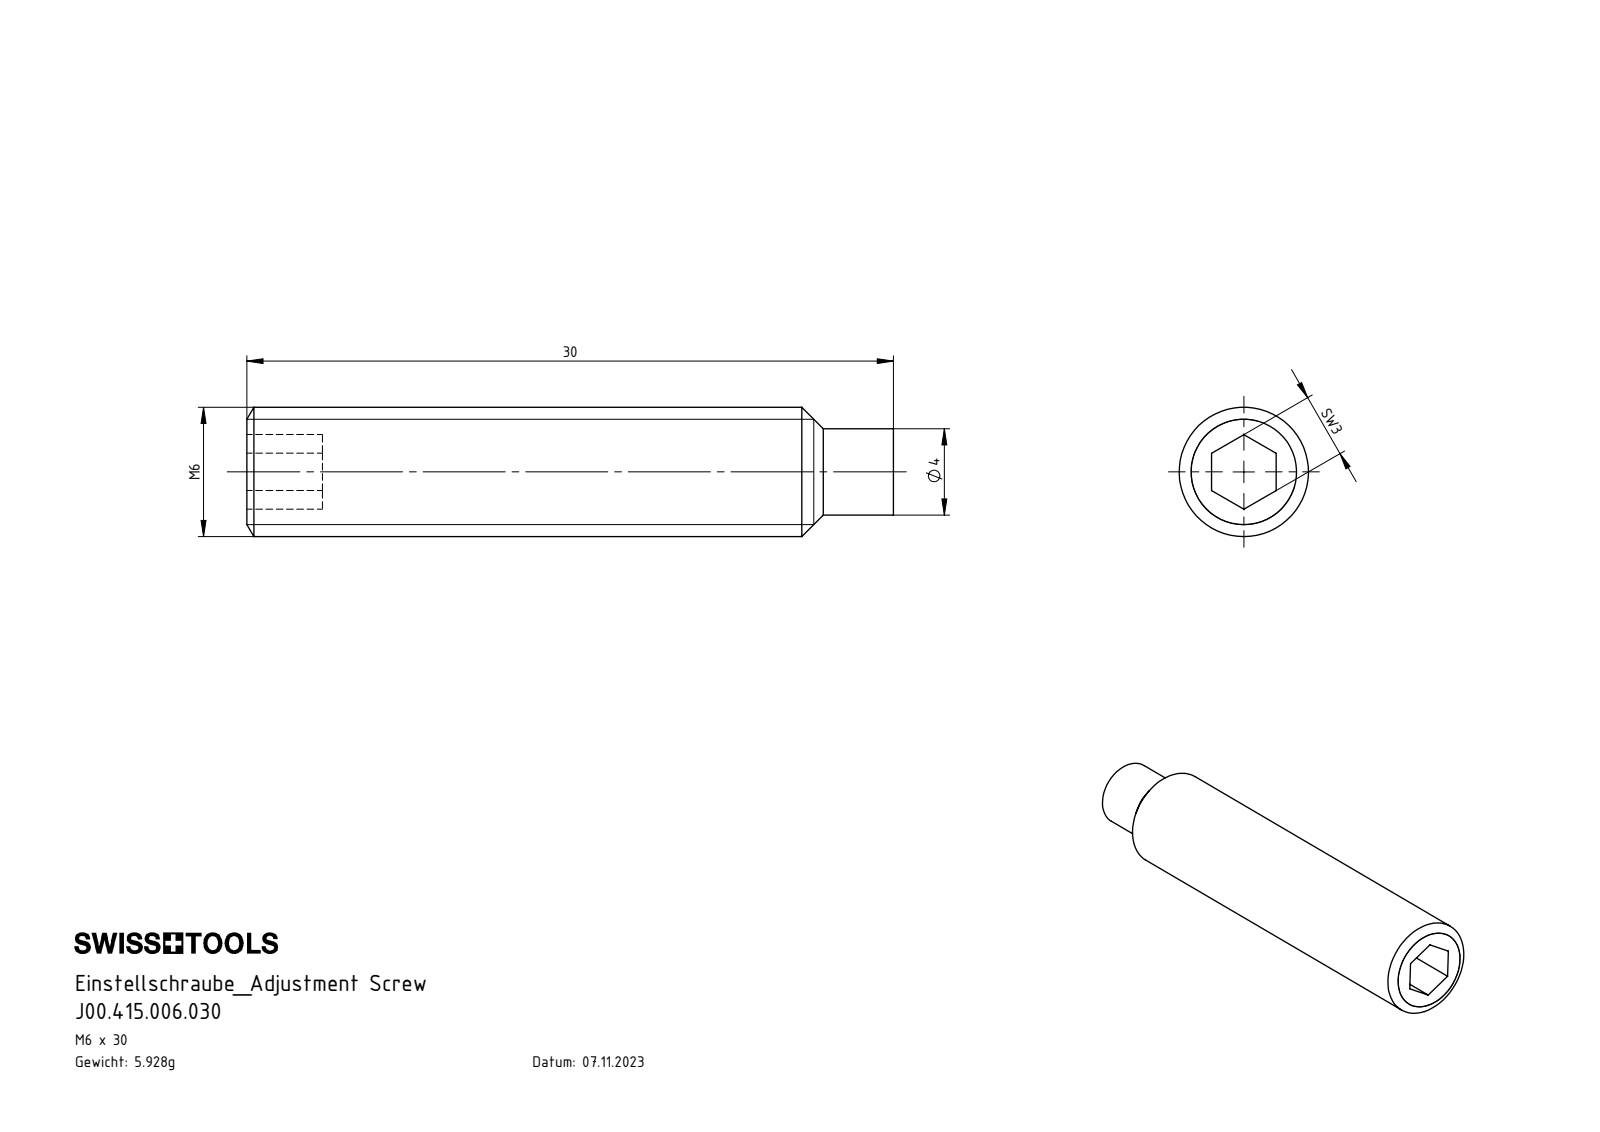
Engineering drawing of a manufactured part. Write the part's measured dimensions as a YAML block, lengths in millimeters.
part_name: "J00.415.006.030"
step_written_by: "SolidWorks 2022 (AUTOMOTIVE_DESIGN)"
units: millimeters
bodies: {solids: 1, faces: 17, planar: 9, cylindrical: 4, other: 4}
overall_size: [30, 6, 6]
volume: 760
surface_area: 621
round_bosses_or_shafts:
  - {diameter: 6, count: 1}
  - {diameter: 4, count: 1}
face_to_face_distances: [3, 30, 3.5, 26.5]
